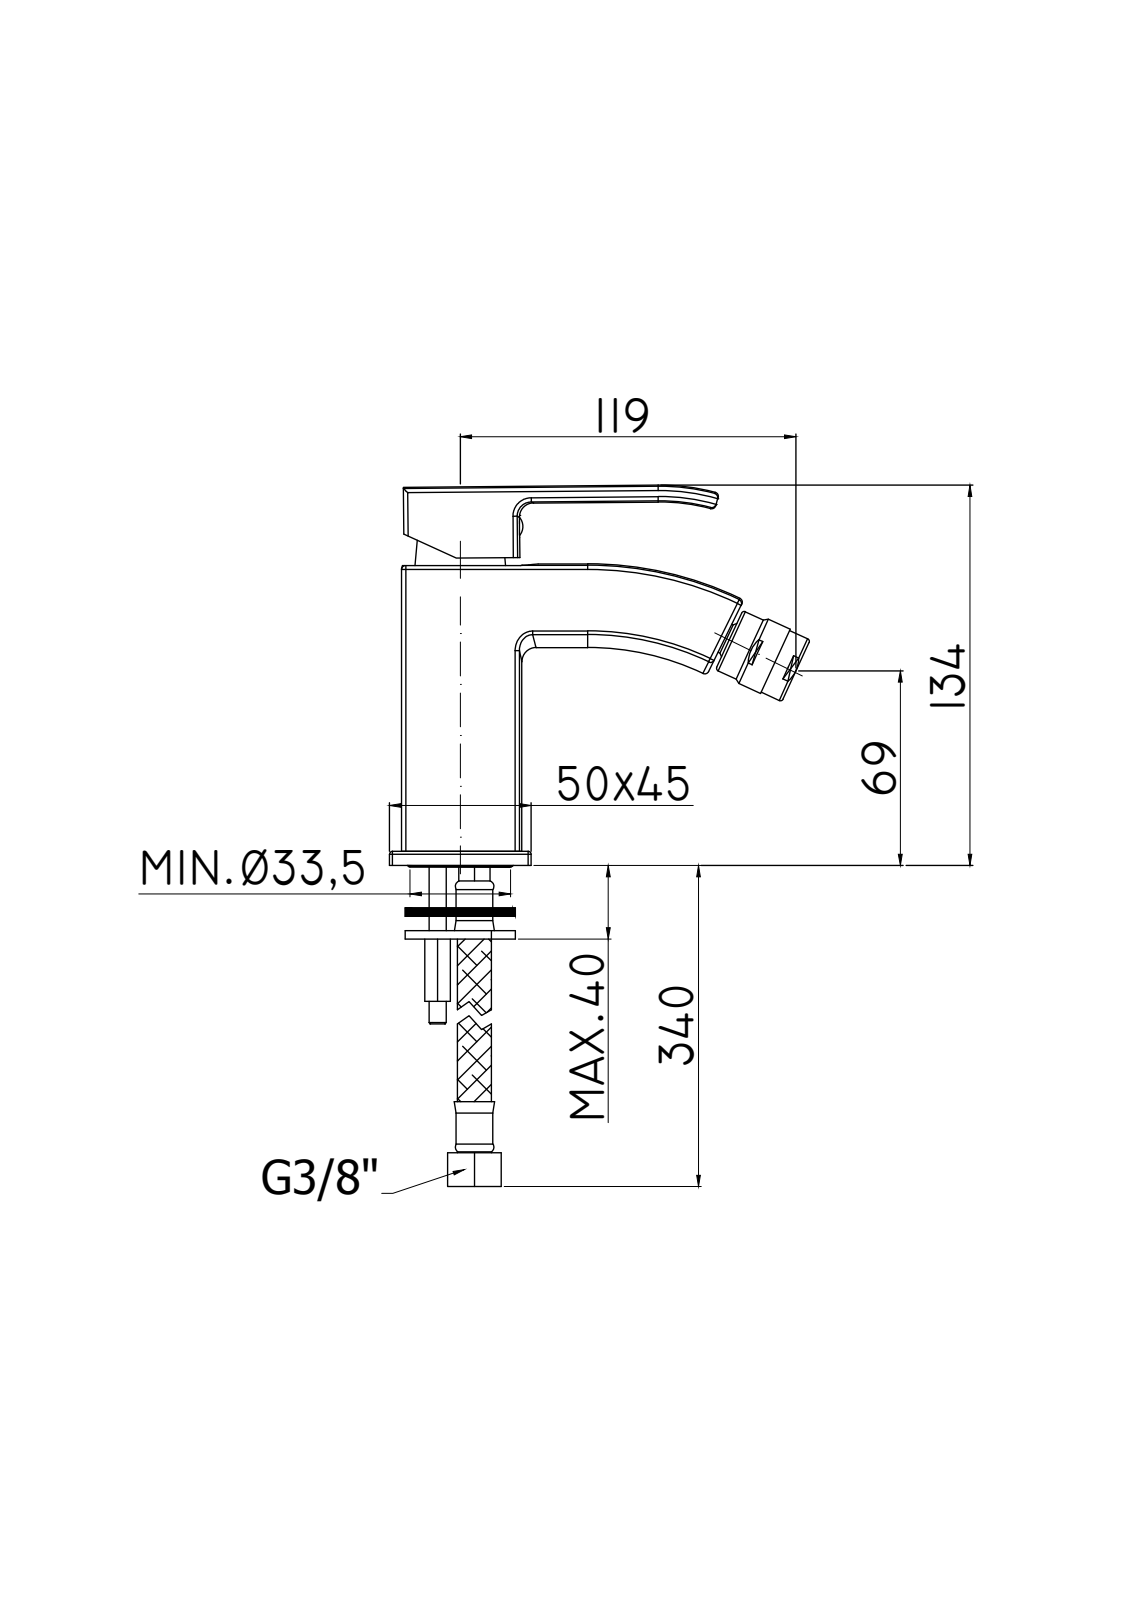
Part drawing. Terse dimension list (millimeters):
name: LES131CR
written by: CREO PARAMETRIC BY PTC INC, 2020044 (CONFIG_CONTROL_DESIGN)
unit: mm
bodies: 2 solids, 2407 faces (1675 planar, 377 cylindrical, 355 other)
size: 148.56 × 134.03 × 45
volume: 173 497 mm³; area: 88 879 mm²
holes: 2× ⌀5, 2× ⌀5.25, 2× ⌀6.2, 2× ⌀9, 2× ⌀11, 2× ⌀16, 1× ⌀3, 1× ⌀4.2, 1× ⌀5.5, 1× ⌀7.8, 1× ⌀8, 1× ⌀15.5
bosses: 2× ⌀24, 1× ⌀38.8, 1× ⌀31.5, 1× ⌀30, 1× ⌀25.8, 1× ⌀25, 1× ⌀23.8, 1× ⌀22.6
rounds: 56× R0.5, 26× R1.5, 25× R1, 16× R2, 10× R0.7, 6× R0.8, 4× R0.6, 4× R0.65
face distances: 3.75, 32.75, 36.5, 29, 5, 3, 0.75, 35.75, 32, 33.5
hole spacings: 2.76, 6.72, 9.01, 12.25, 13.46, 13.6, 14.2, 20.26
